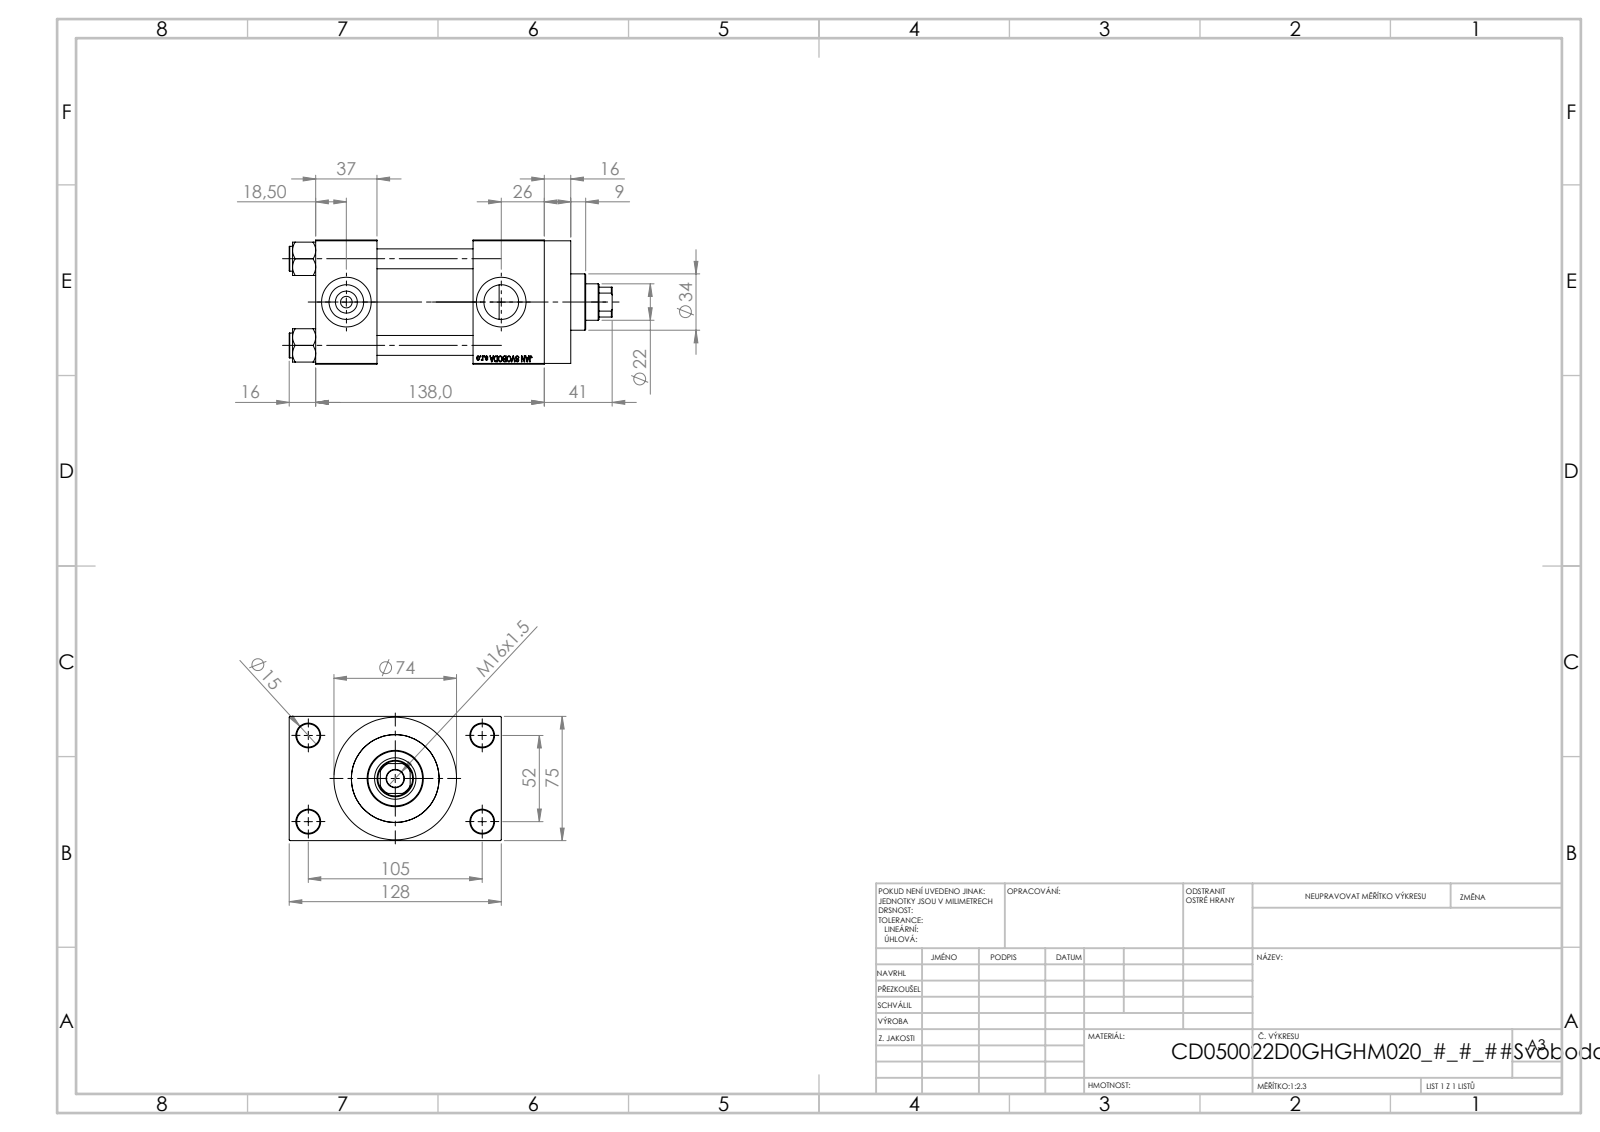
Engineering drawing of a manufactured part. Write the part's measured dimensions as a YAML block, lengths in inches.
part_name: "V215CD_VC_A; V215CD_D_TYCINKA; V215CD_D_Body; V215CD_VCP_D (+1 more)"
step_written_by: "SolidWorks 2019 (CONFIG_CONTROL_DESIGN)"
units: inches
bodies: {solids: 11, faces: 1103, planar: 497, cylindrical: 88, other: 518}
overall_size: [7.677, 5.039, 2.953]
volume: 48.67
surface_area: 258.4
round_holes:
  - {diameter: 0.472, count: 4}
  - {diameter: 0.551, count: 4}
  - {diameter: 0.276, count: 2}
  - {diameter: 0.825, count: 2}
  - {diameter: 1.181, count: 2}
  - {diameter: 0.413, count: 1}
  - {diameter: 0.866, count: 1}
  - {diameter: 0.984, count: 1}
  - {diameter: 1.614, count: 1}
  - {diameter: 1.969, count: 1}
  - {diameter: 2.087, count: 1}
round_bosses_or_shafts:
  - {diameter: 0.591, count: 4}
  - {diameter: 2.913, count: 1}
  - {diameter: 2.205, count: 1}
  - {diameter: 1.339, count: 1}
partial_cylinders:
  - {radius: 0.413, count: 1}
face_to_face_distances: [2.953, 2.283, 1.457, 3.74, 1.043, 5.433, 3.976, 1.693, 3.996, 0.63]
hole_center_spacings: [1.037, 1.456, 2.059, 2.3, 2.307, 3.096, 3.715, 2.047]
